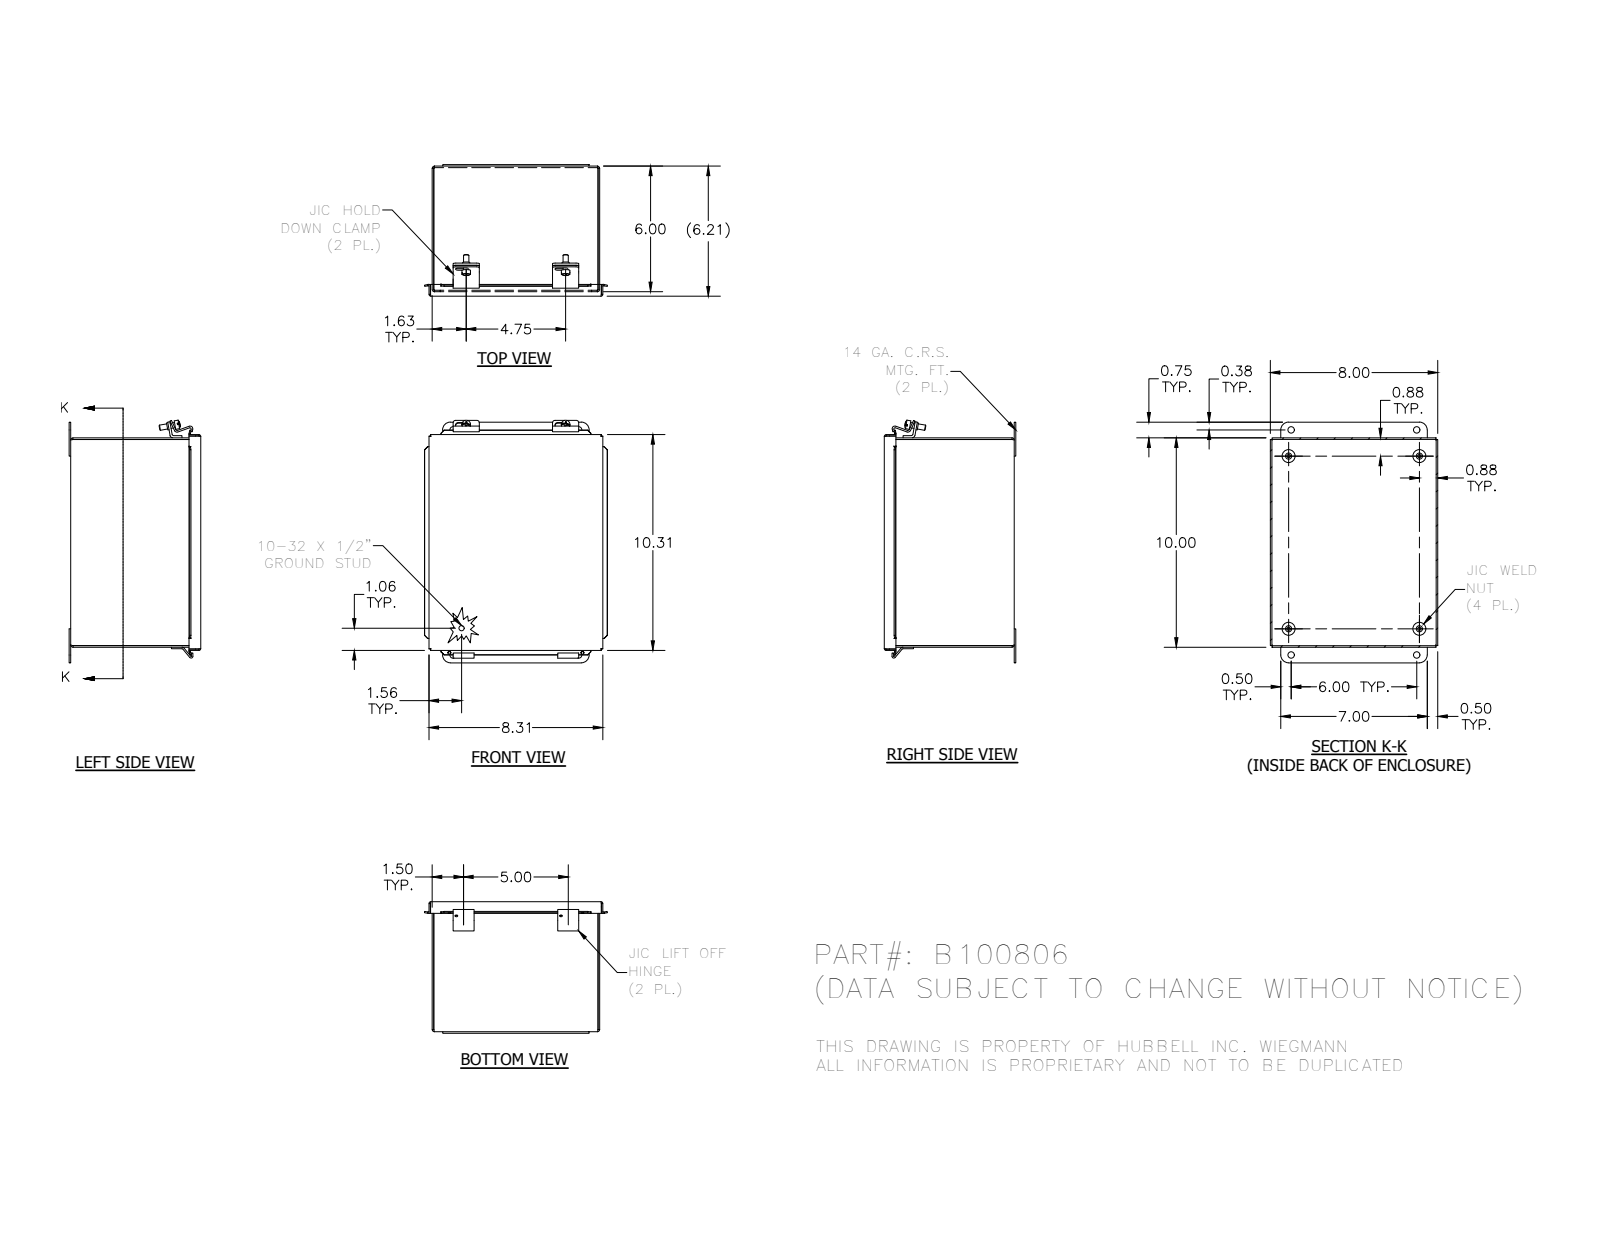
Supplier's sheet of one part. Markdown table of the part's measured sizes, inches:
| quantity | value |
| --- | --- |
| part name | B100806; 3499; 3483; C1001 (+7 more) |
| STEP written by | Autodesk Inventor 2012 (AUTOMOTIVE_DESIGN) |
| units | inches |
| bodies | 19 solids, 422 faces (279 planar, 98 cylindrical, 45 other) |
| overall size | 11.593 × 8.739 × 6.287 |
| volume | 35.62 in³ |
| surface area | 956 in² |
| round holes (diameter × count) | 0.156 × 4, 0.31 × 4, 0.125 × 2, 0.14 × 2, 0.196 × 2 |
| round bosses / shafts (diameter × count) | 0.625 × 4, 0.3 × 4, 0.25 × 3, 0.41 × 2, 0.344 × 2, 0.19 × 1 |
| partial cylindrical surfaces (radius × count) | 0.031 × 16, 0.093 × 8, 0.105 × 8, 0.125 × 8, 0.133 × 4, 0.375 × 4, 0.063 × 3, 0.126 × 3 |
| main face-to-face distances | 0.074, 7.926, 6.15, 9.926, 0.062, 6.212, 6.076, 6.138, 8, 7.852 |
| hole center spacings | 1.256, 1.257, 6, 6.25, 6.251, 8.25, 9.5, 9.501 |
